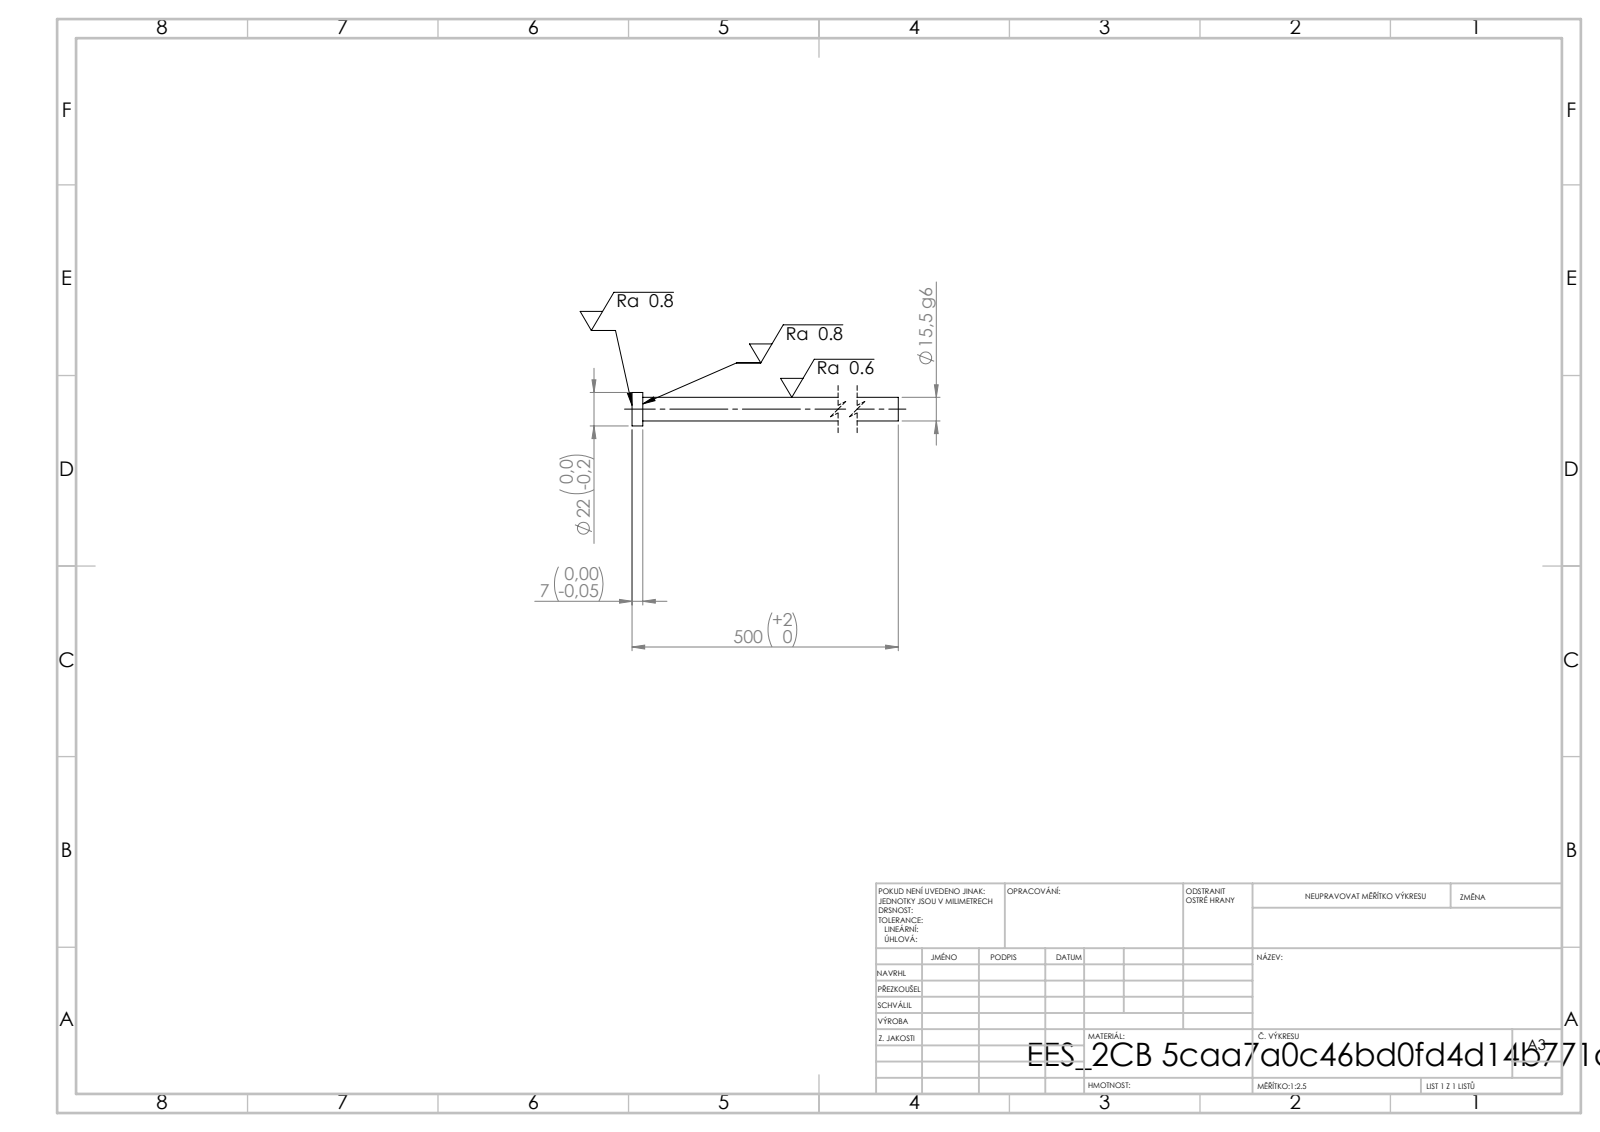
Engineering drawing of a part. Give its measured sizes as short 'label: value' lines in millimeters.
written by: SolidWorks 2019 (CONFIG_CONTROL_DESIGN)
unit: mm
bodies: 1 solid, 7 faces (3 planar, 4 cylindrical, 0 other)
size: 500 × 22 × 22
volume: 95 686 mm³; area: 25 251 mm²
bosses: 1× ⌀22, 1× ⌀15.5
face distances: 7, 500, 493
